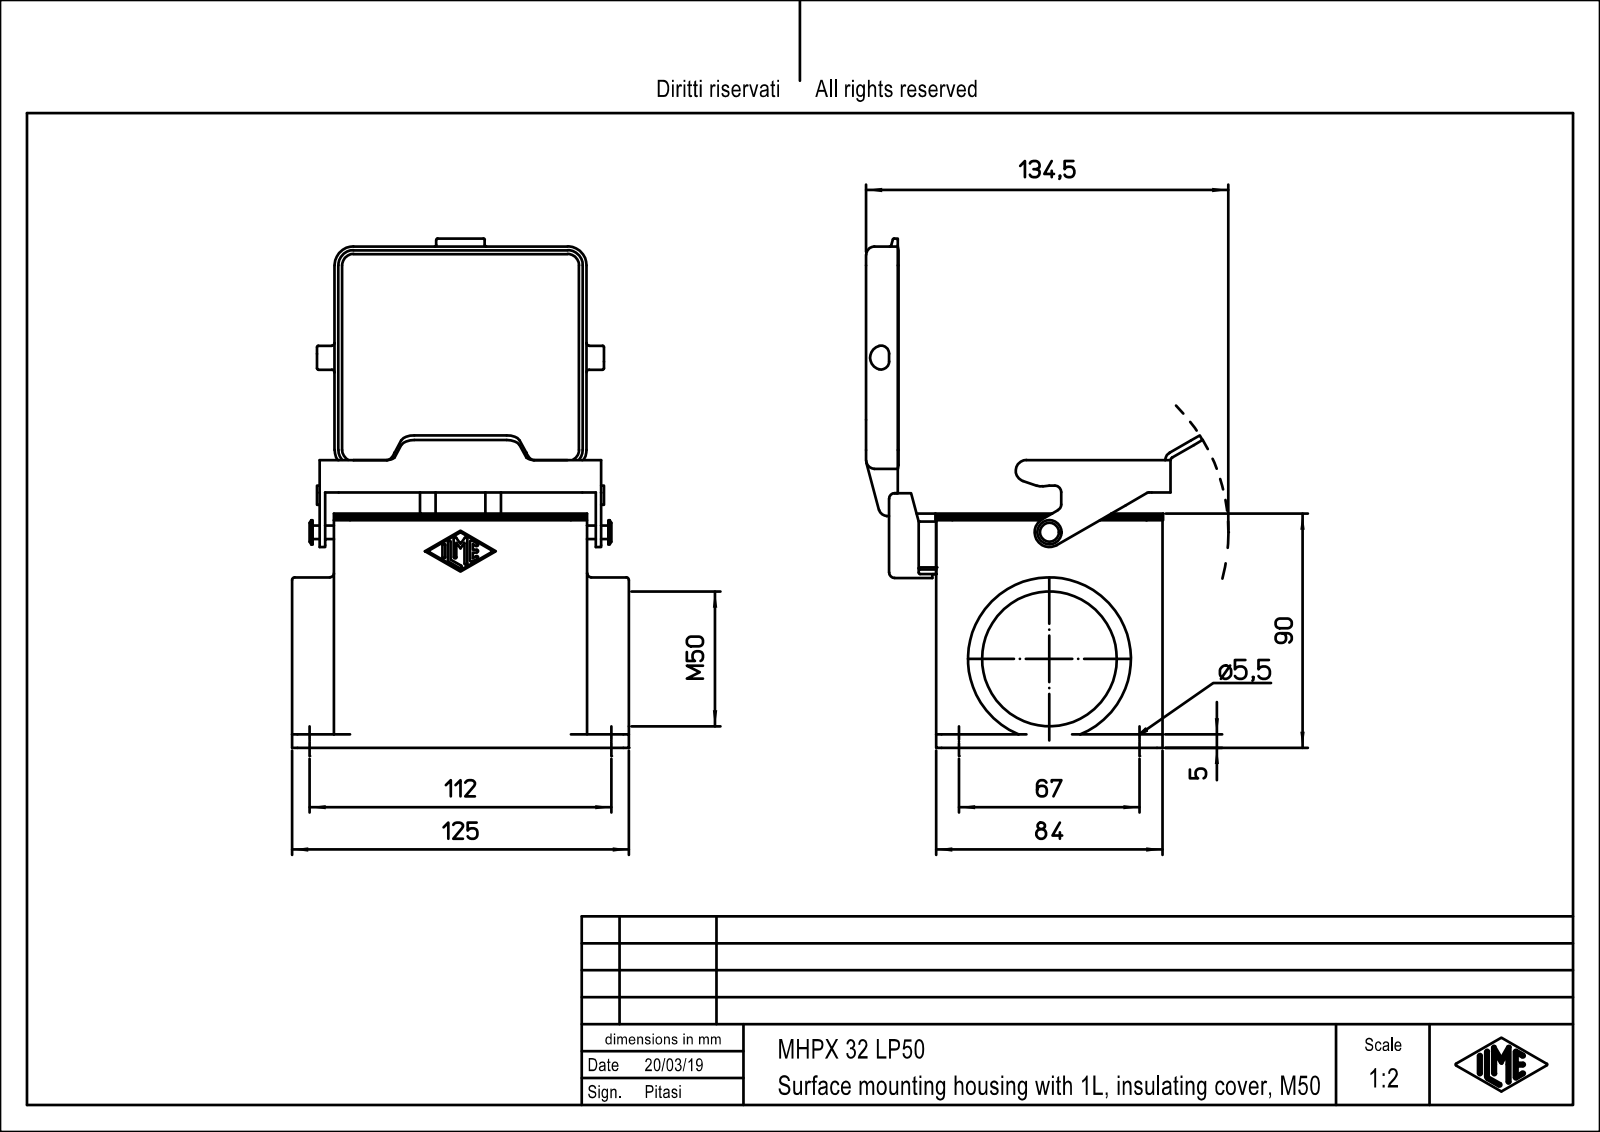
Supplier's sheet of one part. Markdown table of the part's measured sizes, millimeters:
| quantity | value |
| --- | --- |
| part name | CHPX_32_L; MHPX_32_LP50; MHPX_32_LP50.stp |
| STEP written by | PTC Creo Elements/Direct Modeling 19.0E 27-Jun-2016 (C) Parametric Technology GmbH (AUTOMOTIVE_DESIGN) |
| units | millimeters |
| bodies | 1 solid, 337 faces (178 planar, 139 cylindrical, 20 other) |
| overall size | 189 × 125 × 124.86 |
| volume | 255 217 mm³ |
| surface area | 129 309 mm² |
| round holes (diameter × count) | 3 × 8, 5.5 × 4, 4.2 × 1, 30 × 1, 50 × 1 |
| round bosses / shafts (diameter × count) | 60.5 × 1, 9 × 1, 6 × 1, 5 × 1 |
| partial cylindrical surfaces (radius × count) | 3 × 14, 2 × 11, 1.5 × 9, 6 × 8, 0.5 × 6, 7 × 6, 5 × 5, 4.2 × 4 |
| main face-to-face distances | 3, 2, 81, 4, 27, 84, 110, 108, 24, 26 |
| hole center spacings | 17.37, 27, 33.74, 36, 41.73, 67.25, 77.5, 82.07 |
